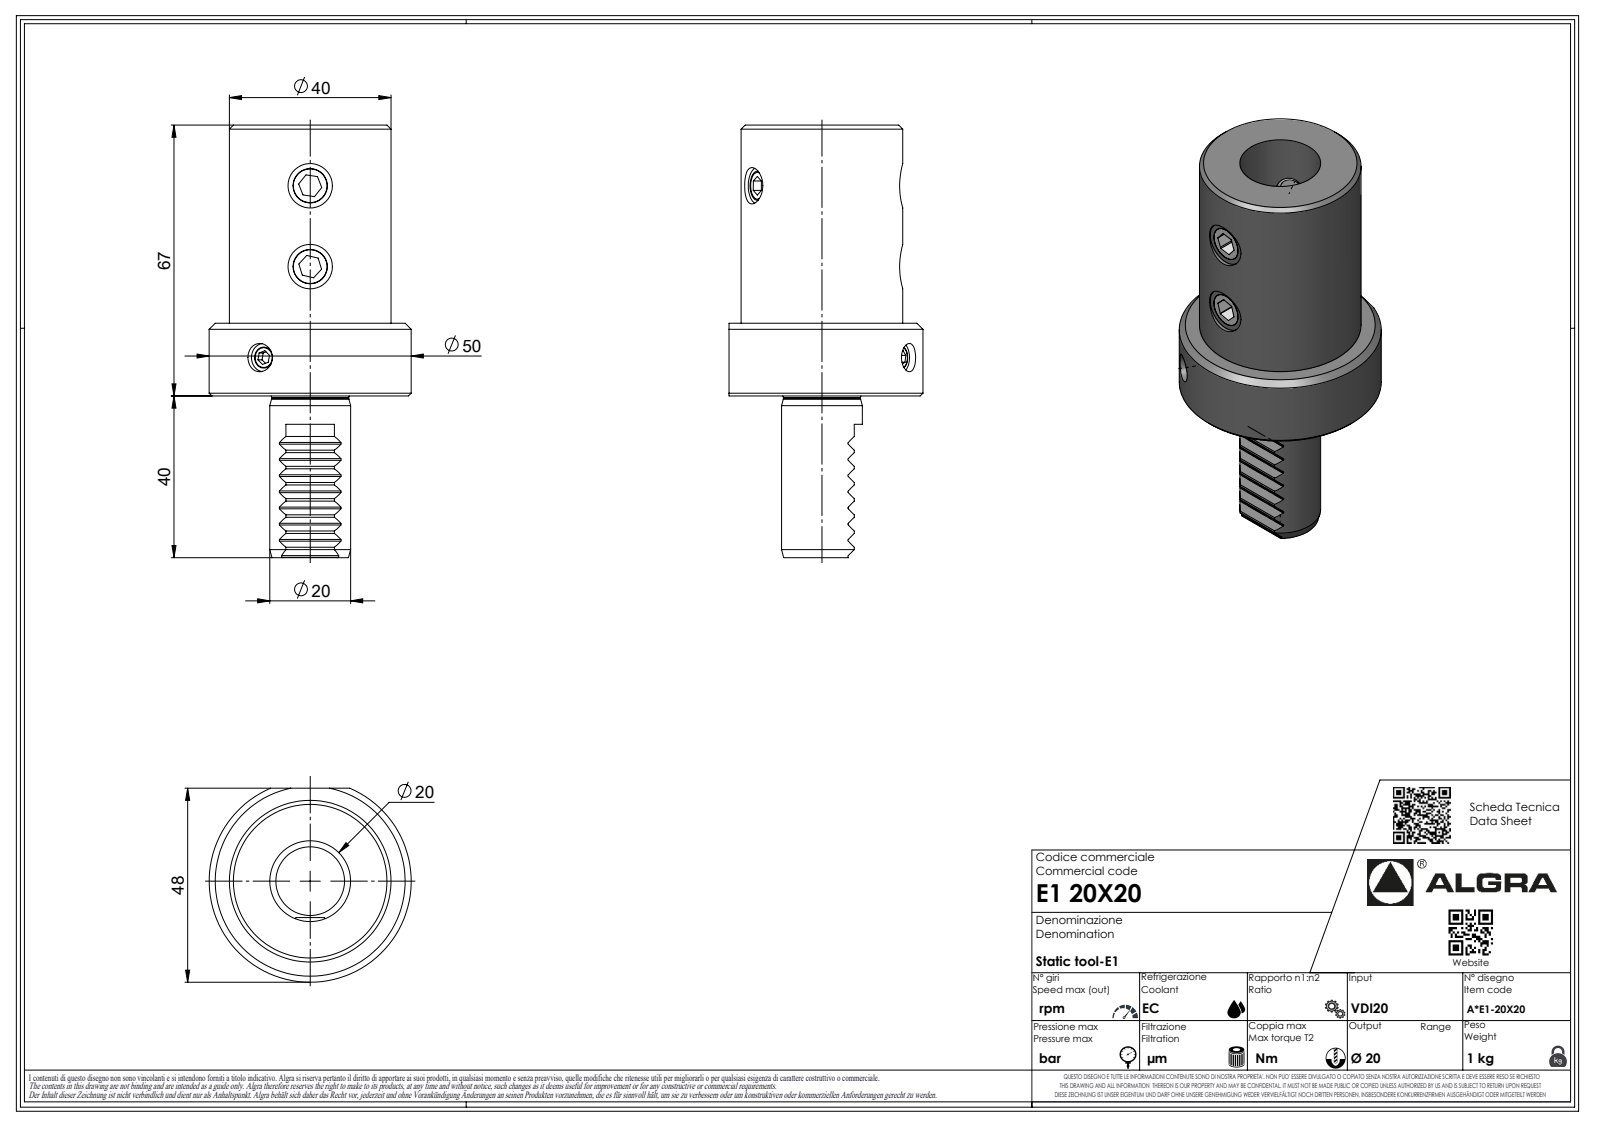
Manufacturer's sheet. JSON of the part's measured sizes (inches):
{"part_name": "E120X20", "step_written_by": "SolidWorks 2023 (AUTOMOTIVE_DESIGN)", "units": "inches", "bodies": {"solids": 1, "faces": 254, "planar": 172, "cylindrical": 39, "other": 43}, "overall_size": [4.213, 1.969, 1.89], "volume_in3": 5.341, "surface_area_in2": 29.6, "round_holes": [[0.083, 1], [0.787, 1]], "round_bosses_or_shafts": [[1.969, 1], [1.575, 1], [0.752, 1], [0.251, 1], [0.067, 1]], "partial_cylinders_radius": [[0.012, 8], [0.013, 7], [0.02, 7], [0.146, 7], [0.008, 1]], "face_to_face_distances": [2.638, 0.709, 1.929, 0.197, 0.236, 0.472, 2.402, 0.111, 1.575, 1.811]}
